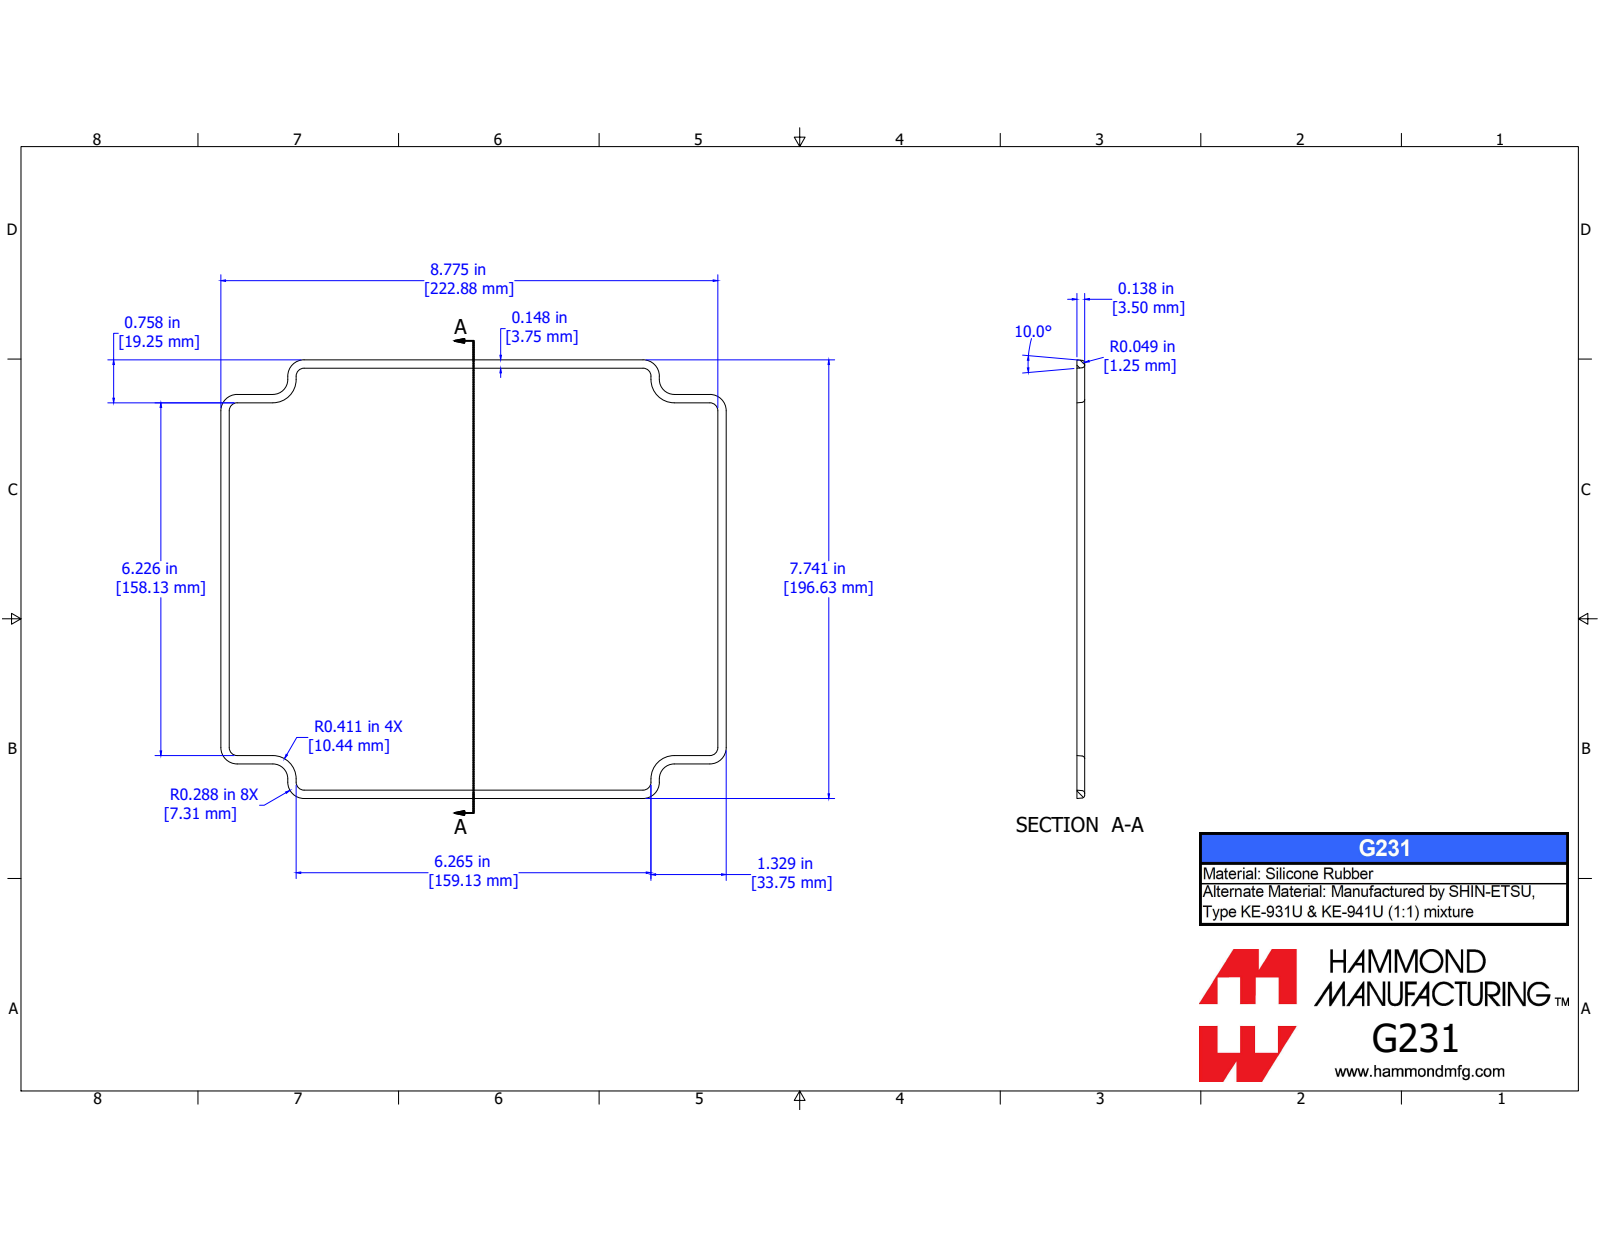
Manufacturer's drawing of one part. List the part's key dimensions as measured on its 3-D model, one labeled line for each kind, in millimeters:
Part name (STEP PRODUCT): 1590Z231G
STEP written by: SolidWorks 2019 (CONFIG_CONTROL_DESIGN)
Units: millimetres
Bodies: 1 solid, 98 faces (26 planar, 24 cylindrical, 48 other)
Overall size (bounding box): 226.1 × 196.1 × 3.5
Volume: 8 440 mm³ · Surface area: 9 942 mm²
Partial cylindrical surfaces — rounded edges, fillets, slot ends (radius × count): R1 ×16
Main face-to-face distances: 3.5, 192.9, 222.9, 15.5, 177.4, 161.9, 30, 162.9
